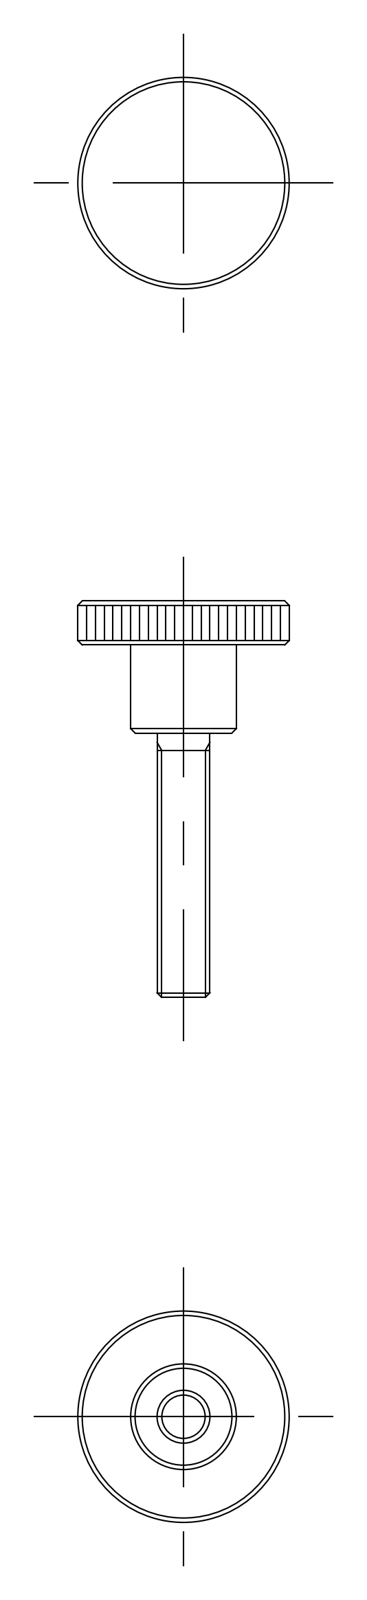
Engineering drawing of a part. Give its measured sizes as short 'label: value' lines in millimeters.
name: knob
written by: CADfix (AUTOMOTIVE_DESIGN)
unit: mm
bodies: 1 solid, 18 faces (0 planar, 0 cylindrical, 18 other)
size: 45 × 24 × 24
volume: 4 224 mm³; area: 2 163 mm²
